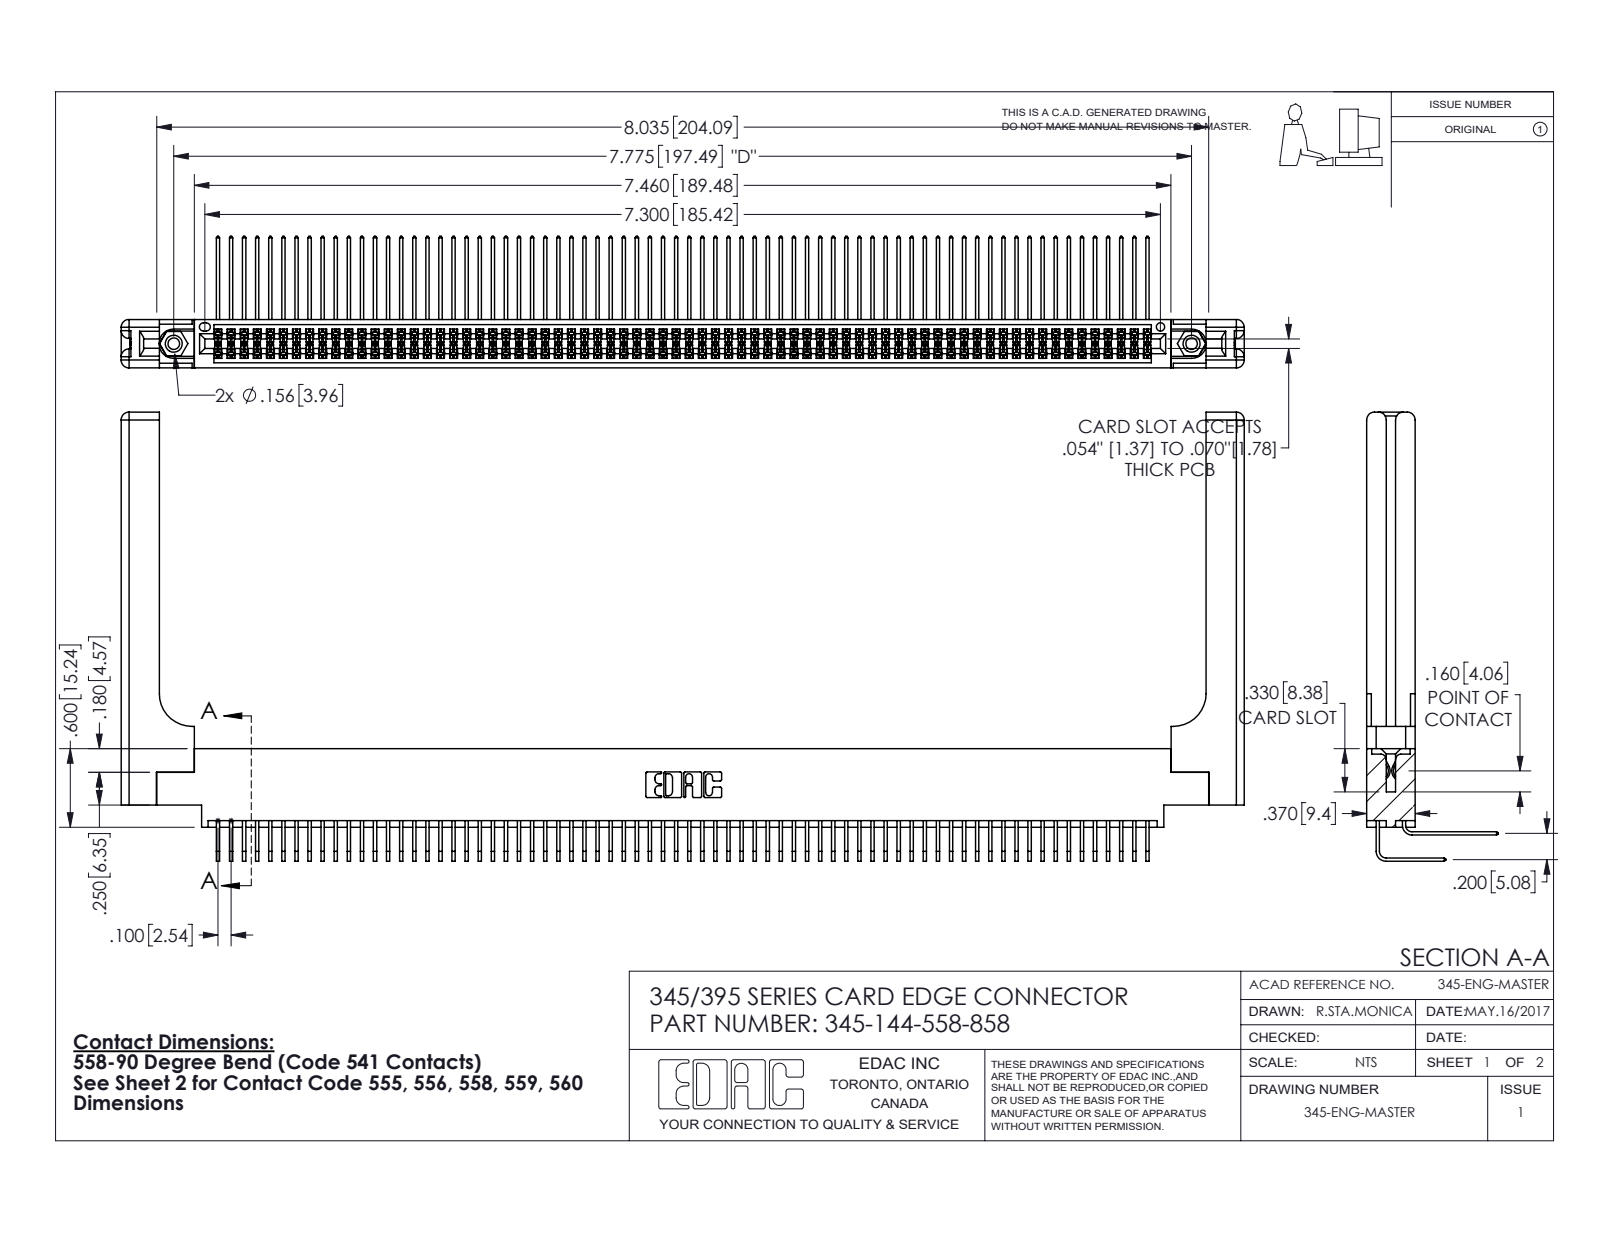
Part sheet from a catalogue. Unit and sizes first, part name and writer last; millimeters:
Units: millimetres
Overall size (bounding box): 217.9 × 87.1 × 25.5
Round holes (diameter × count): ⌀2.3 ×2, ⌀3.2 ×2, ⌀4 ×2, ⌀1.6 ×1
Round bosses / shafts (diameter × count): ⌀3.9 ×2
Partial cylindrical surfaces — rounded edges, fillets, slot ends (radius × count): R0.2 ×216, R0.3 ×22, R1.5 ×16, R0.2 ×6, R0.8 ×6, R0.7 ×3, R0.4 ×2, R0.5 ×2
Main face-to-face distances: 1.8, 7.6, 9.4, 5.1, 2.5, 6.9, 0.6, 5.7, 4.4, 0.6
Hole centre spacings: 6.9, 191.5, 197.5
Volume: 30 640 mm³ · Surface area: 42 450 mm²
Bodies: 149 solids, 7874 faces (5272 planar, 2542 cylindrical, 60 other)
Part name (STEP PRODUCT): 345-220-058_345-220-058; 345 Part_0.170 Offset - 0.156 Dia-TH; 345-250-001_345-250-001-102; 345-292-001_558 Tail - 2 (+2 more)
STEP written by: SolidWorks 2016 (CONFIG_CONTROL_DESIGN)
